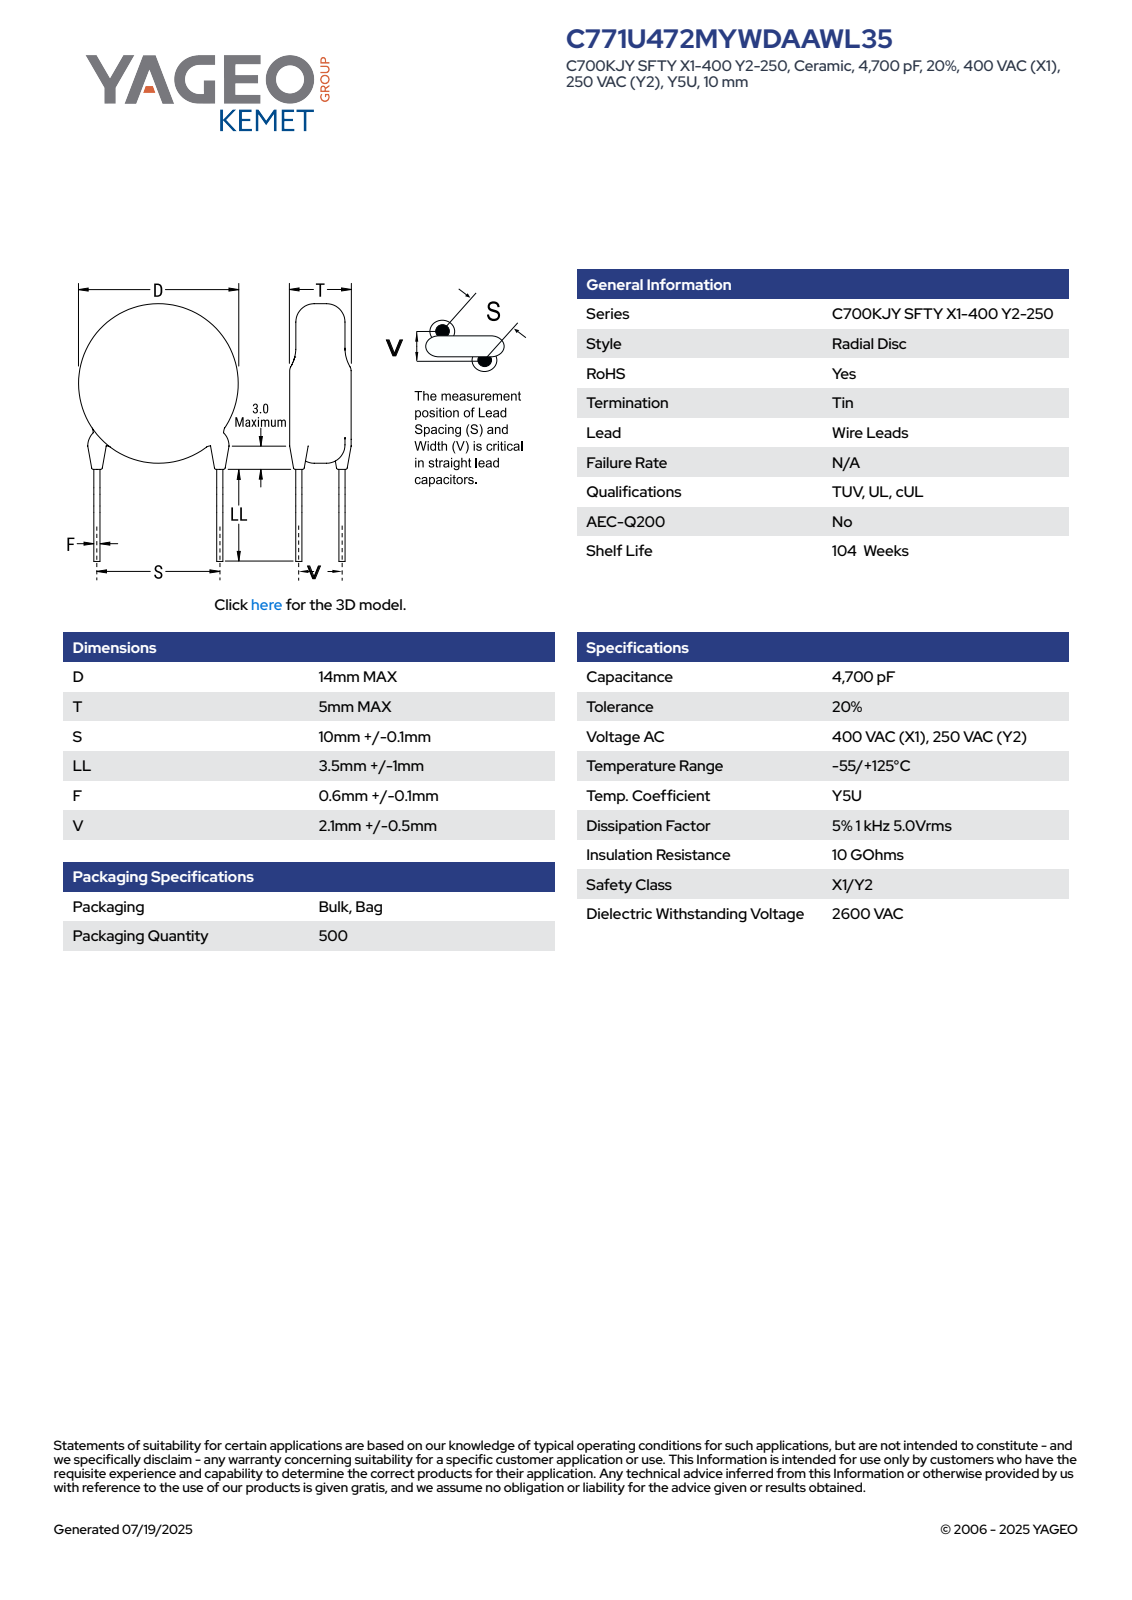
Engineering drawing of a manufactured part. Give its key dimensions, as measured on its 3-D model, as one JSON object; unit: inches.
{"part_name": "CCD_KST_14X5_D14T5S11LL4.5F0.7V2.1", "step_written_by": "SolidWorks 2021 (AUTOMOTIVE_DESIGN)", "units": "inches", "bodies": {"solids": 4, "faces": 77, "planar": 63, "cylindrical": 10, "other": 4}, "overall_size": [0.743, 0.551, 0.197], "volume_in3": 0.046, "surface_area_in2": 0.842, "round_bosses_or_shafts": [[0.047, 2], [0.028, 2], [0.551, 1]], "face_to_face_distances": [0.197, 0.177, 0.515, 0.338, 0.45, 0.273, 0.065, 0.018, 0.265, 0.013]}
